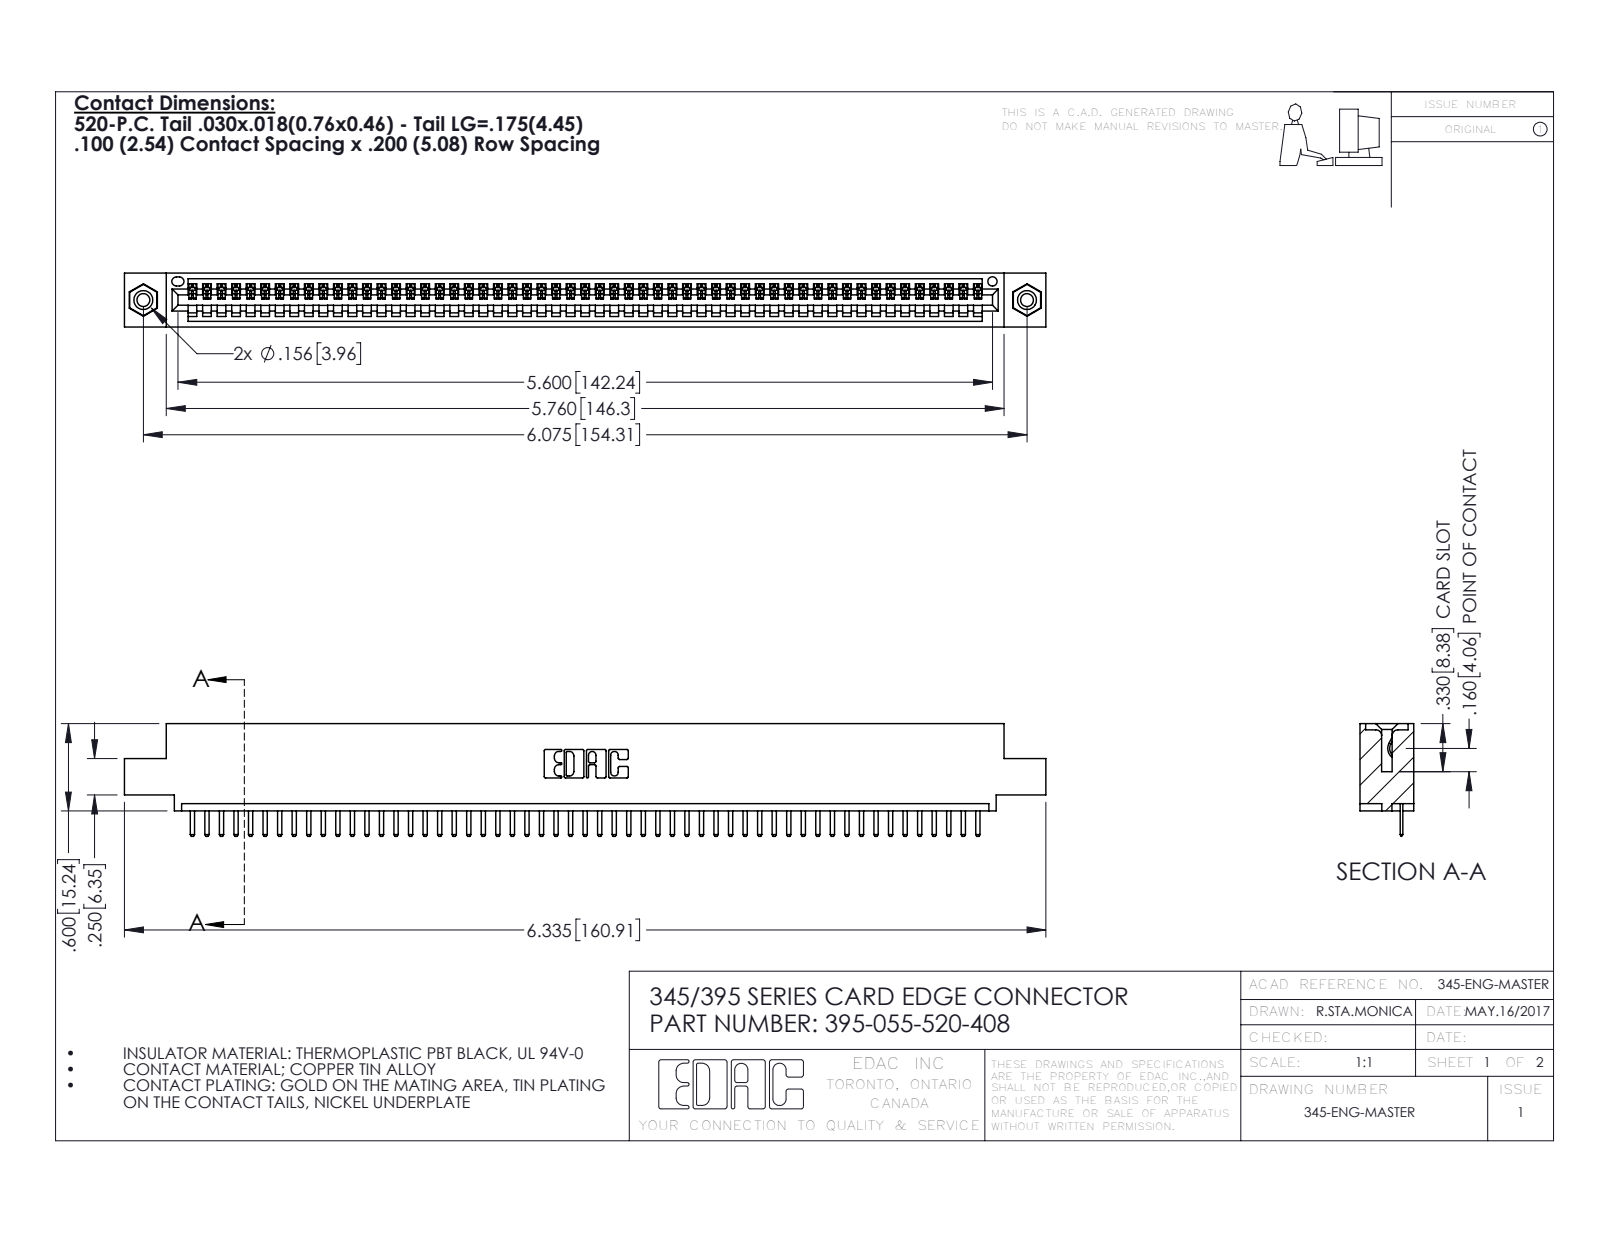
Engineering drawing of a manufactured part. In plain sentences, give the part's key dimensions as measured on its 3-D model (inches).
The part is named "395-055-520-408; 345-292-001_345-293-120; 345 Part_0.110 Offset - 0.156 Dia-TI; 345-250-001_345-250-003-102". Its 3-D file was written by "SolidWorks 2016 (CONFIG_CONTROL_DESIGN)". It is 58 solids with 3600 faces: 2426 planar, 1158 cylindrical and 16 other. Overall it measures 6.335 by 0.775 by 0.37 inches. Its volume is 0.925 cubic inches and its surface area 30.84 square inches. Round holes: 2 of diameter 0.089, 2 of diameter 0.125, 2 of diameter 0.156, 1 of diameter 0.064. Round bosses or shafts: 2 of diameter 0.155. Partial cylindrical surfaces (rounded edges, fillets, slot ends): 112 of radius 0.01, 110 of radius 0.006, 22 of radius 0.01, 6 of radius 0.007, 6 of radius 0.031, 3 of radius 0.026, 2 of radius 0.031, 2 of radius 0.04. The main face-to-face distances are 0.072, 0.298, 0.37, 0.2, 0.098, 0.272, 0.025, 0.225, 0.072, 0.149. The hole center spacings are 0.27, 5.839, 6.075.
